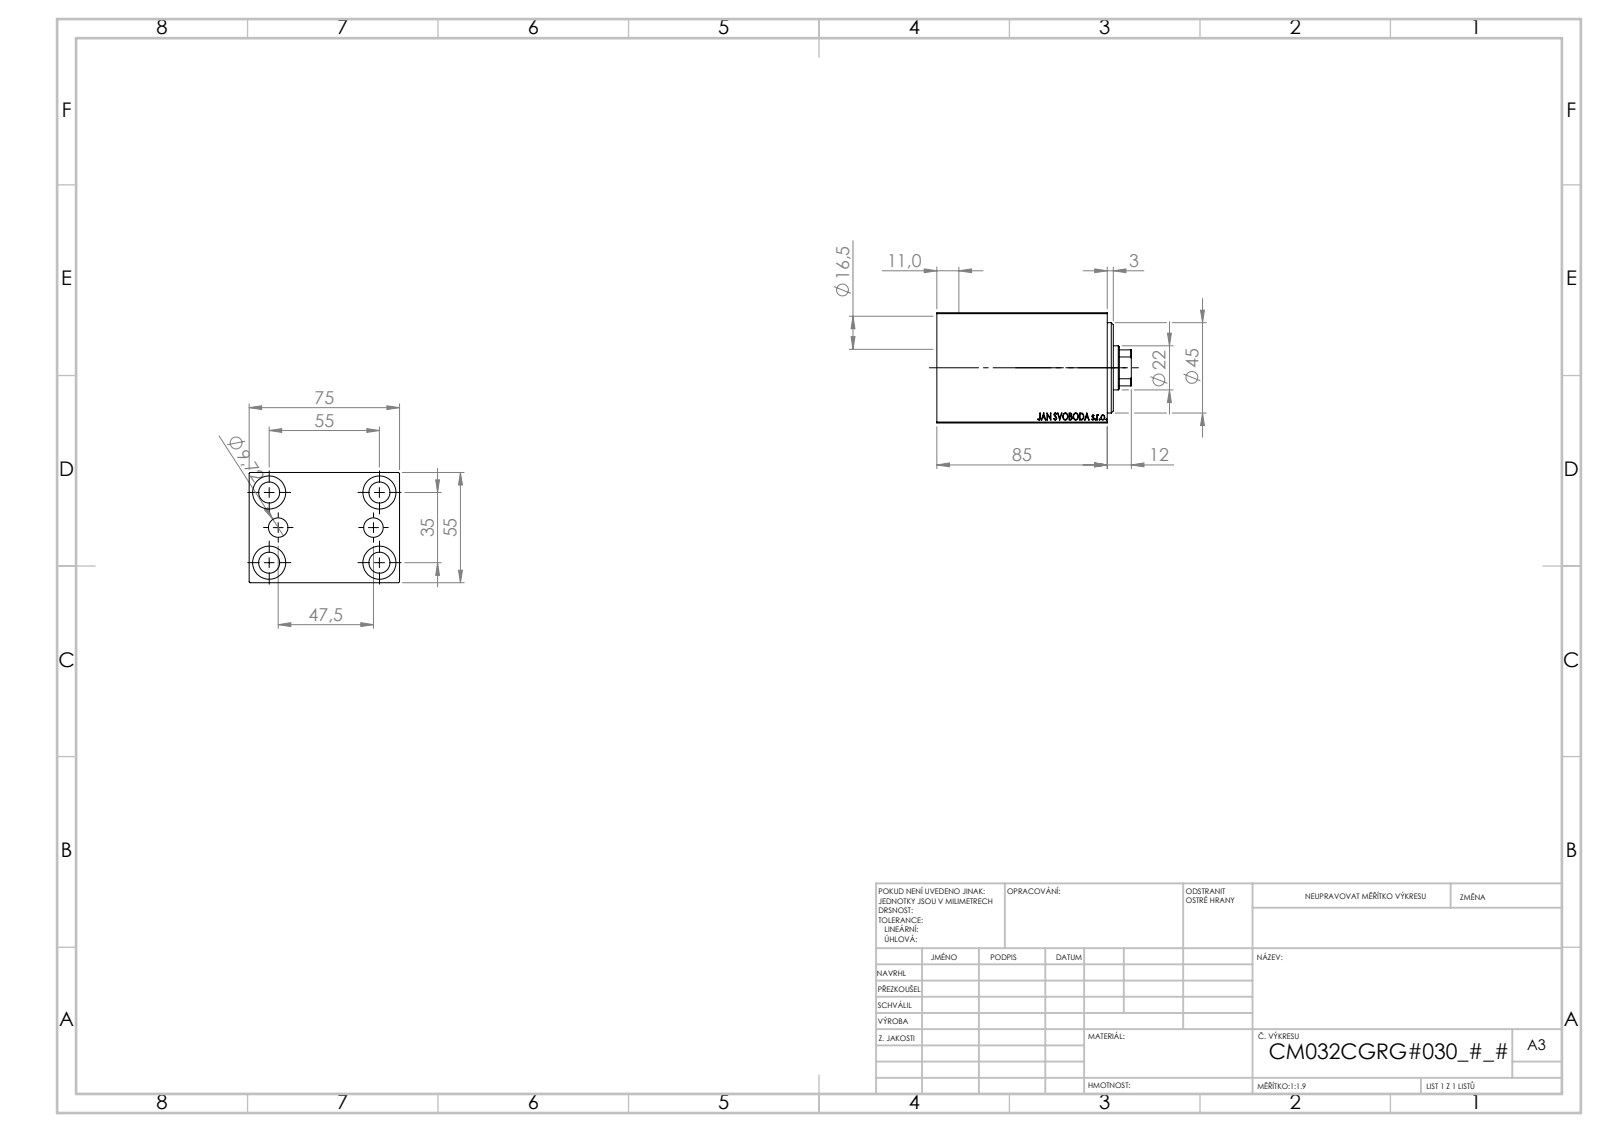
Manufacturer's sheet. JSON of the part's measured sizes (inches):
{"part_name": "V450CM_C_VCP; V450CM_VC_B; V450CM_C_Body", "step_written_by": "SolidWorks 2019 (CONFIG_CONTROL_DESIGN)", "units": "inches", "bodies": {"solids": 3, "faces": 858, "planar": 408, "cylindrical": 56, "other": 394}, "overall_size": [3.819, 2.953, 2.165], "volume_in3": 18.29, "surface_area_in2": 97.68, "round_holes": [[0.413, 5], [0.65, 4], [0.157, 2], [0.383, 2], [0.866, 1], [1.004, 1], [1.26, 1], [1.339, 1], [1.772, 1]], "partial_cylinders_radius": [[0.413, 1]], "face_to_face_distances": [2.165, 2.953, 0.197, 1.132, 2.215, 3.346, 3.15, 2.018, 0.433, 2.913], "hole_center_spacings": [0.705, 1.283, 2.132, 0.935, 1.378, 2.165, 2.567, 1.87]}
